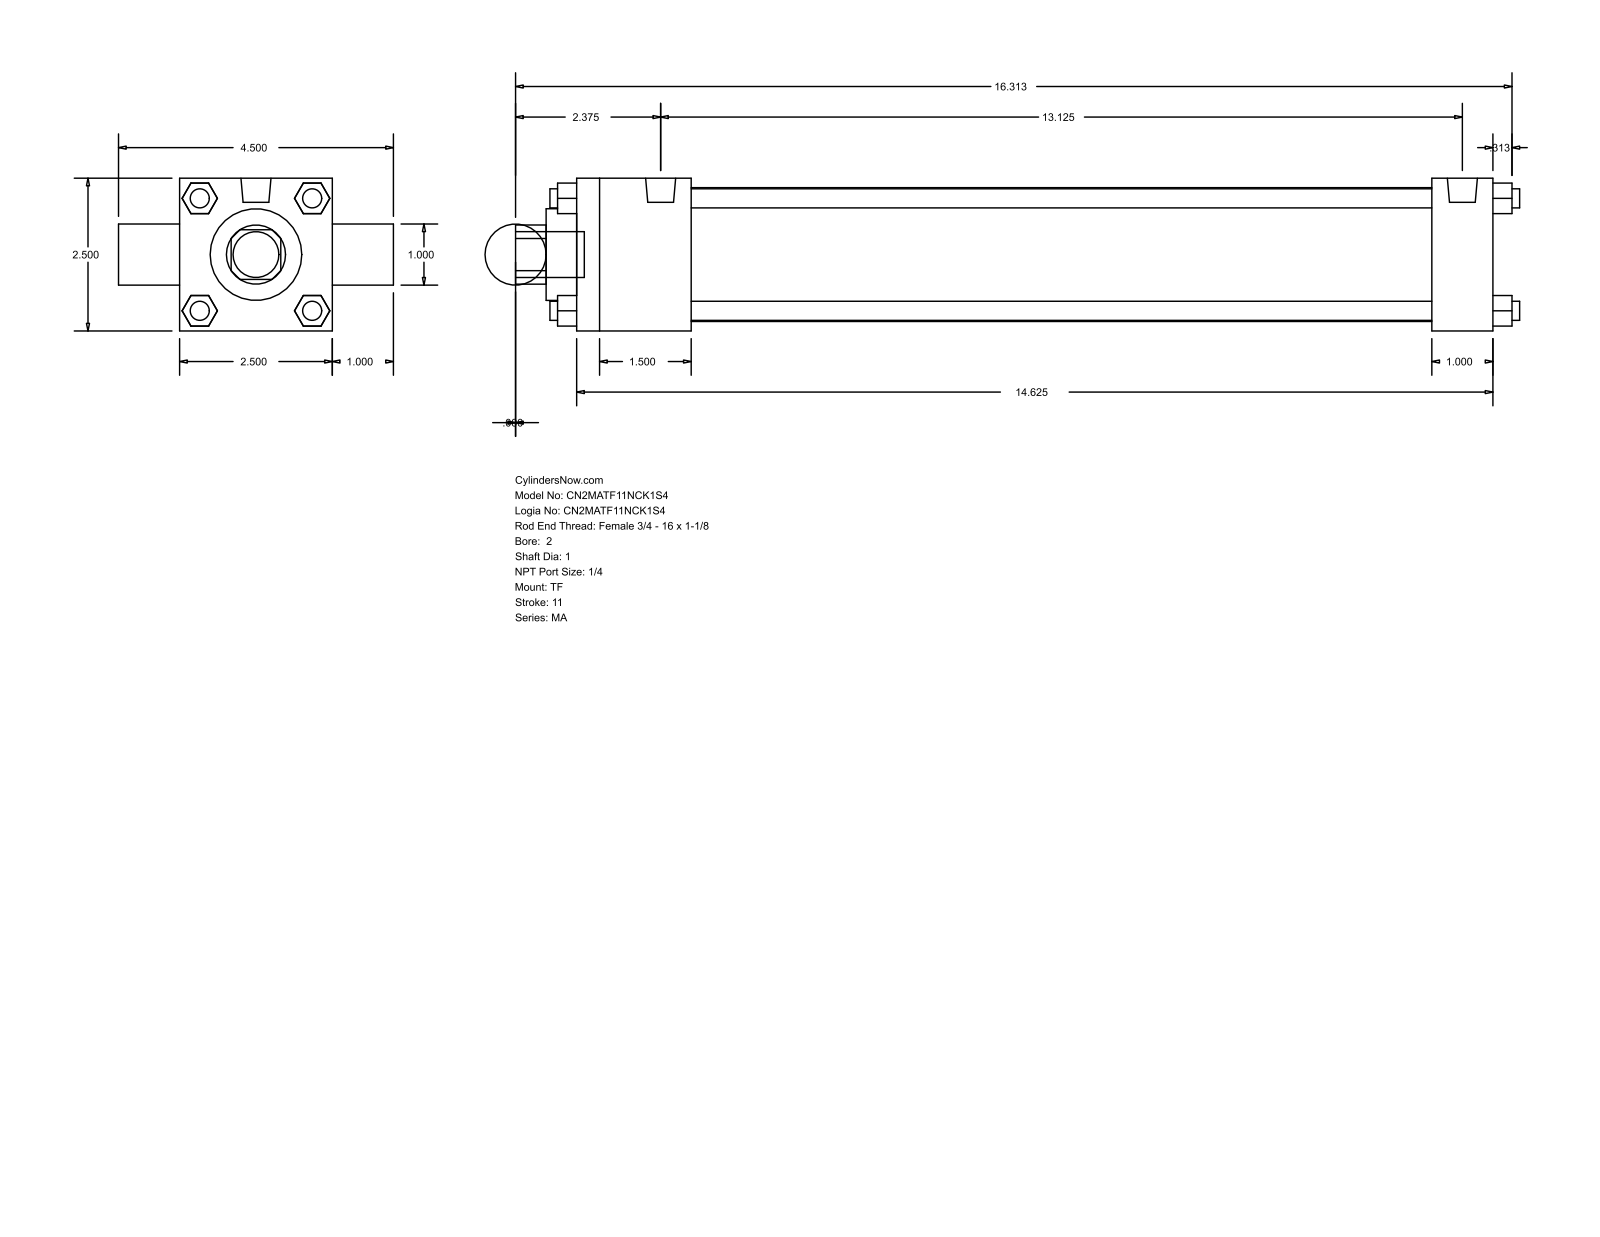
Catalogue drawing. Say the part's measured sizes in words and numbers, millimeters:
The part is named "MA_TF__0200_1". Its 3-D file was written by "GSSL Pune (CONFIG_CONTROL_DESIGN)". It is 0 solids with 120 faces: 92 planar, 28 cylindrical and 0 other. Overall it measures 417.51 by 114.3 by 63.5 millimeters. Round holes: 2 of diameter 25.4, 1 of diameter 38.1, 1 of diameter 55.63. Round bosses or shafts: 7 of diameter 7.94, 2 of diameter 12.49, 1 of diameter 19.05. Partial cylindrical surfaces (rounded edges, fillets, slot ends): 1 of radius 12.29. The main face-to-face distances are 63.5, 25.4, 381, 12.7, 47.63, 355.6, 307.97, 333.37, 88.9, 23.37.
